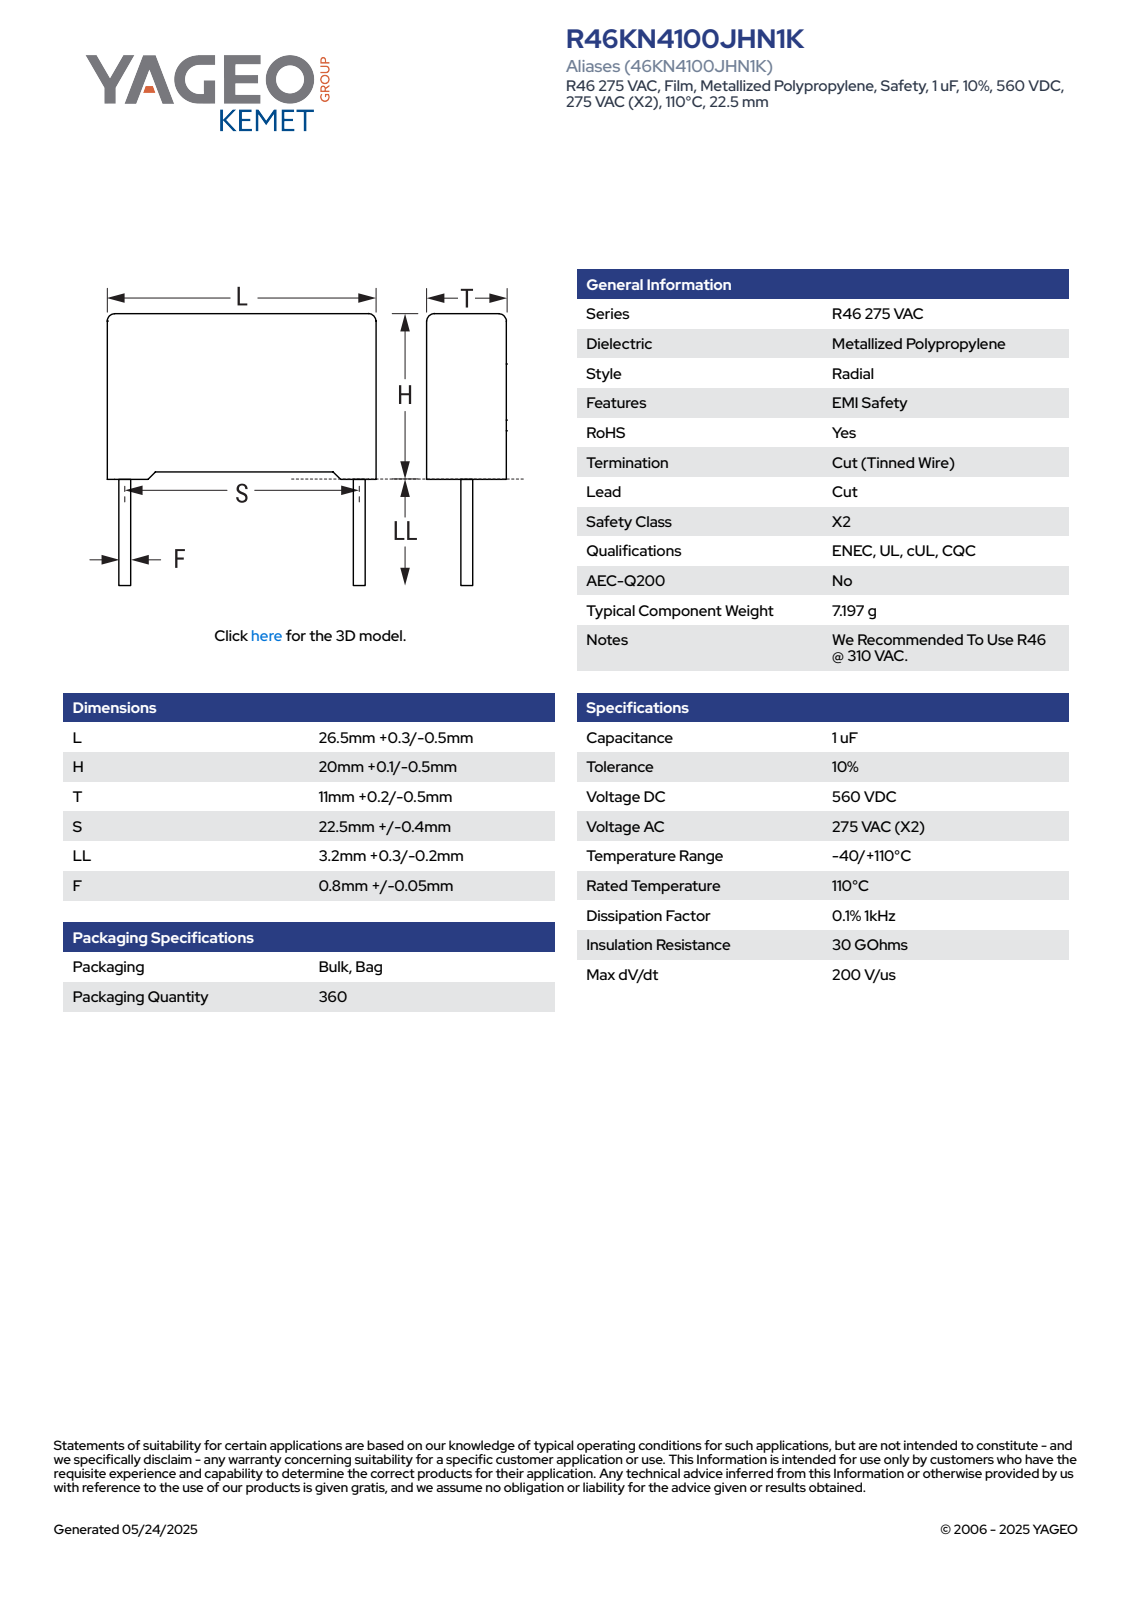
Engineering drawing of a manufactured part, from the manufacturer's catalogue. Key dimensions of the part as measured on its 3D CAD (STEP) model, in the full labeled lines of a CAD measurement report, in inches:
Part name (STEP PRODUCT): CFR_RB2_26.5X20X11_L26.8H20.1T11.2S22.5LL3.5F0.85
STEP written by: SolidWorks 2021 (AUTOMOTIVE_DESIGN)
Units: inches
Bodies: 4 solids, 85 faces (77 planar, 8 cylindrical, 0 other)
Overall size (bounding box): 1.055 × 0.929 × 0.441
Volume: 0.356 in³ · Surface area: 3.393 in²
Round bosses / shafts (diameter × count): ⌀0.033 ×2
Partial cylindrical surfaces — rounded edges, fillets, slot ends (radius × count): R0.02 ×4
Main face-to-face distances: 0.441, 0.762, 1.055, 0.764, 0.03, 0.027, 0.791, 0.035, 1.02, 0.441
